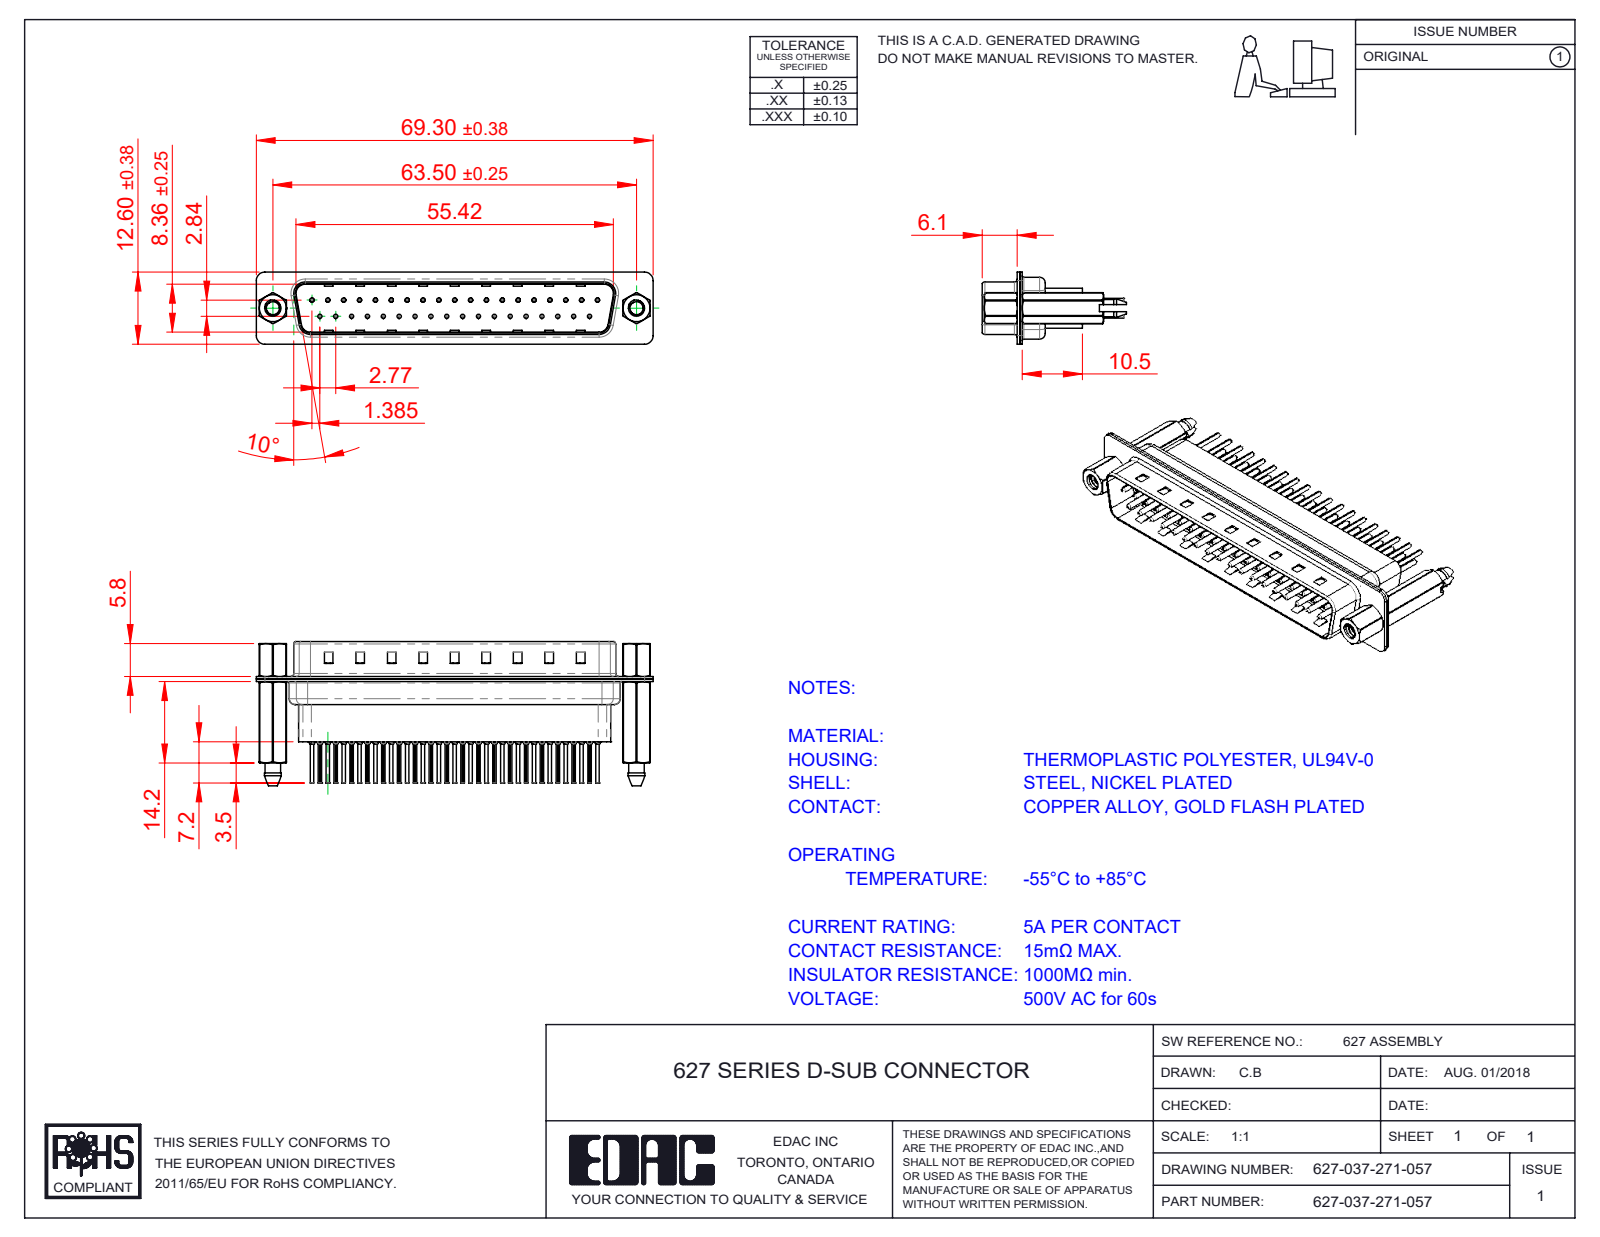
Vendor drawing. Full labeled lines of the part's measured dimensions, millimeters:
Part name (STEP PRODUCT): 627 Shell Rear_37 Contacts; 627 Contact Row 2_61; 627 Housing_37 HP; 627 4-40 Threaded Boardlock_HP71 (+4 more)
STEP written by: SolidWorks 2020 (CONFIG_CONTROL_DESIGN)
Units: millimetres
Bodies: 44 solids, 4272 faces (1145 planar, 1648 cylindrical, 1479 other)
Overall size (bounding box): 69.3 × 25.1 × 12.6
Volume: 5 911 mm³ · Surface area: 15 189 mm²
Round holes (diameter × count): ⌀0.2 ×37, ⌀0.35 ×37, ⌀1.1 ×37, ⌀1.6 ×37, ⌀2.26 ×2, ⌀2.29 ×2, ⌀4 ×2, ⌀4.8 ×2
Round bosses / shafts (diameter × count): ⌀2 ×37, ⌀1.5 ×37, ⌀0.75 ×37, ⌀0.6 ×37, ⌀4.9 ×2, ⌀2.79 ×2
Partial cylindrical surfaces — rounded edges, fillets, slot ends (radius × count): R0.1 ×74, R1.5 ×18, R2 ×12, R1.6 ×10, R0.5 ×8, R0.25 ×4, R0.6 ×4, R0.65 ×4
Main face-to-face distances: 0.4, 0.82, 9.58, 0.45, 0.68, 7.68, 1.5, 1.08, 8.08, 8.76
Hole centre spacings: 3.16, 2.77, 5.54, 8.31, 5.04, 10.1, 11.08, 12.78
